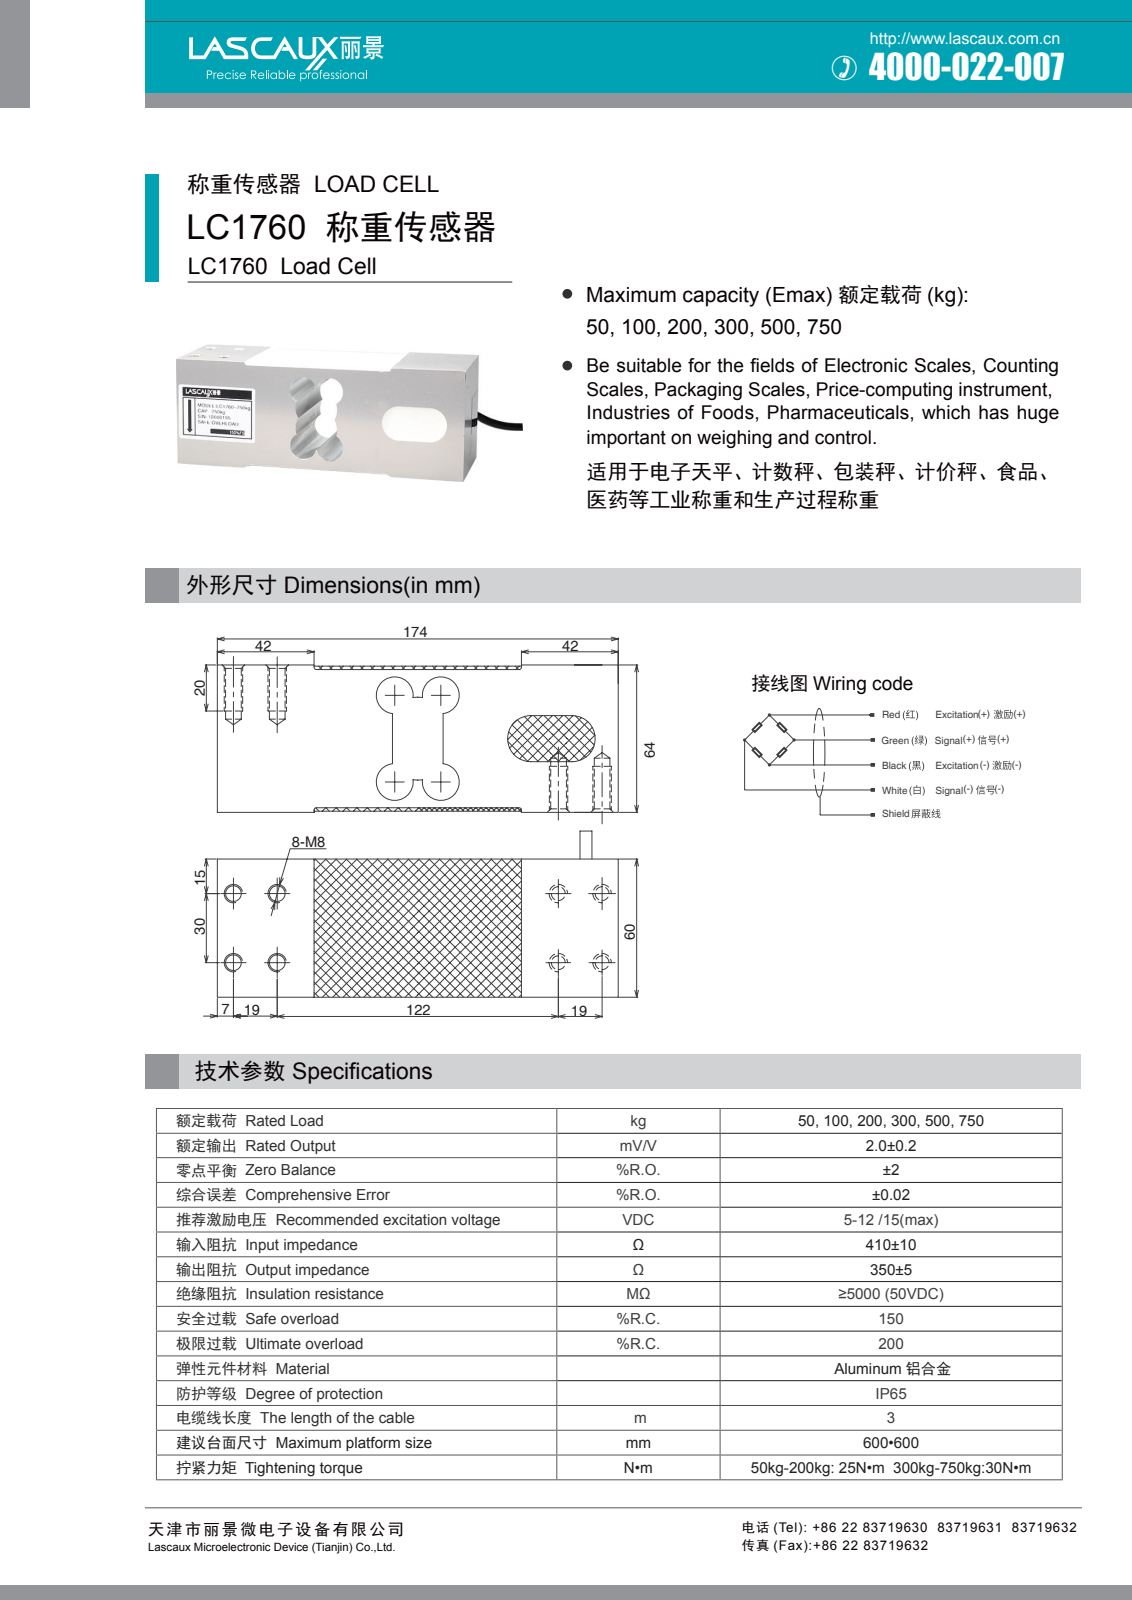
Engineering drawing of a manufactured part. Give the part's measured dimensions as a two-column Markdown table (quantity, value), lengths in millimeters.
| quantity | value |
| --- | --- |
| part name | LC1760 |
| STEP written by | SolidWorks 2016 (CONFIG_CONTROL_DESIGN) |
| units | millimeters |
| bodies | 1 solid, 60 faces (18 planar, 26 cylindrical, 16 other) |
| overall size | 174 × 64 × 60 |
| volume | 563 267 mm³ |
| surface area | 63 176 mm² |
| round holes (diameter × count) | 6.8 × 8 |
| partial cylindrical surfaces (radius × count) | 1 × 4, 7.5 × 4 |
| main face-to-face distances | 60, 2, 62, 64, 174, 77, 97, 20, 13, 51 |
| hole center spacings | 19, 30, 35.51, 141, 144.16, 122, 125.63, 160 |
